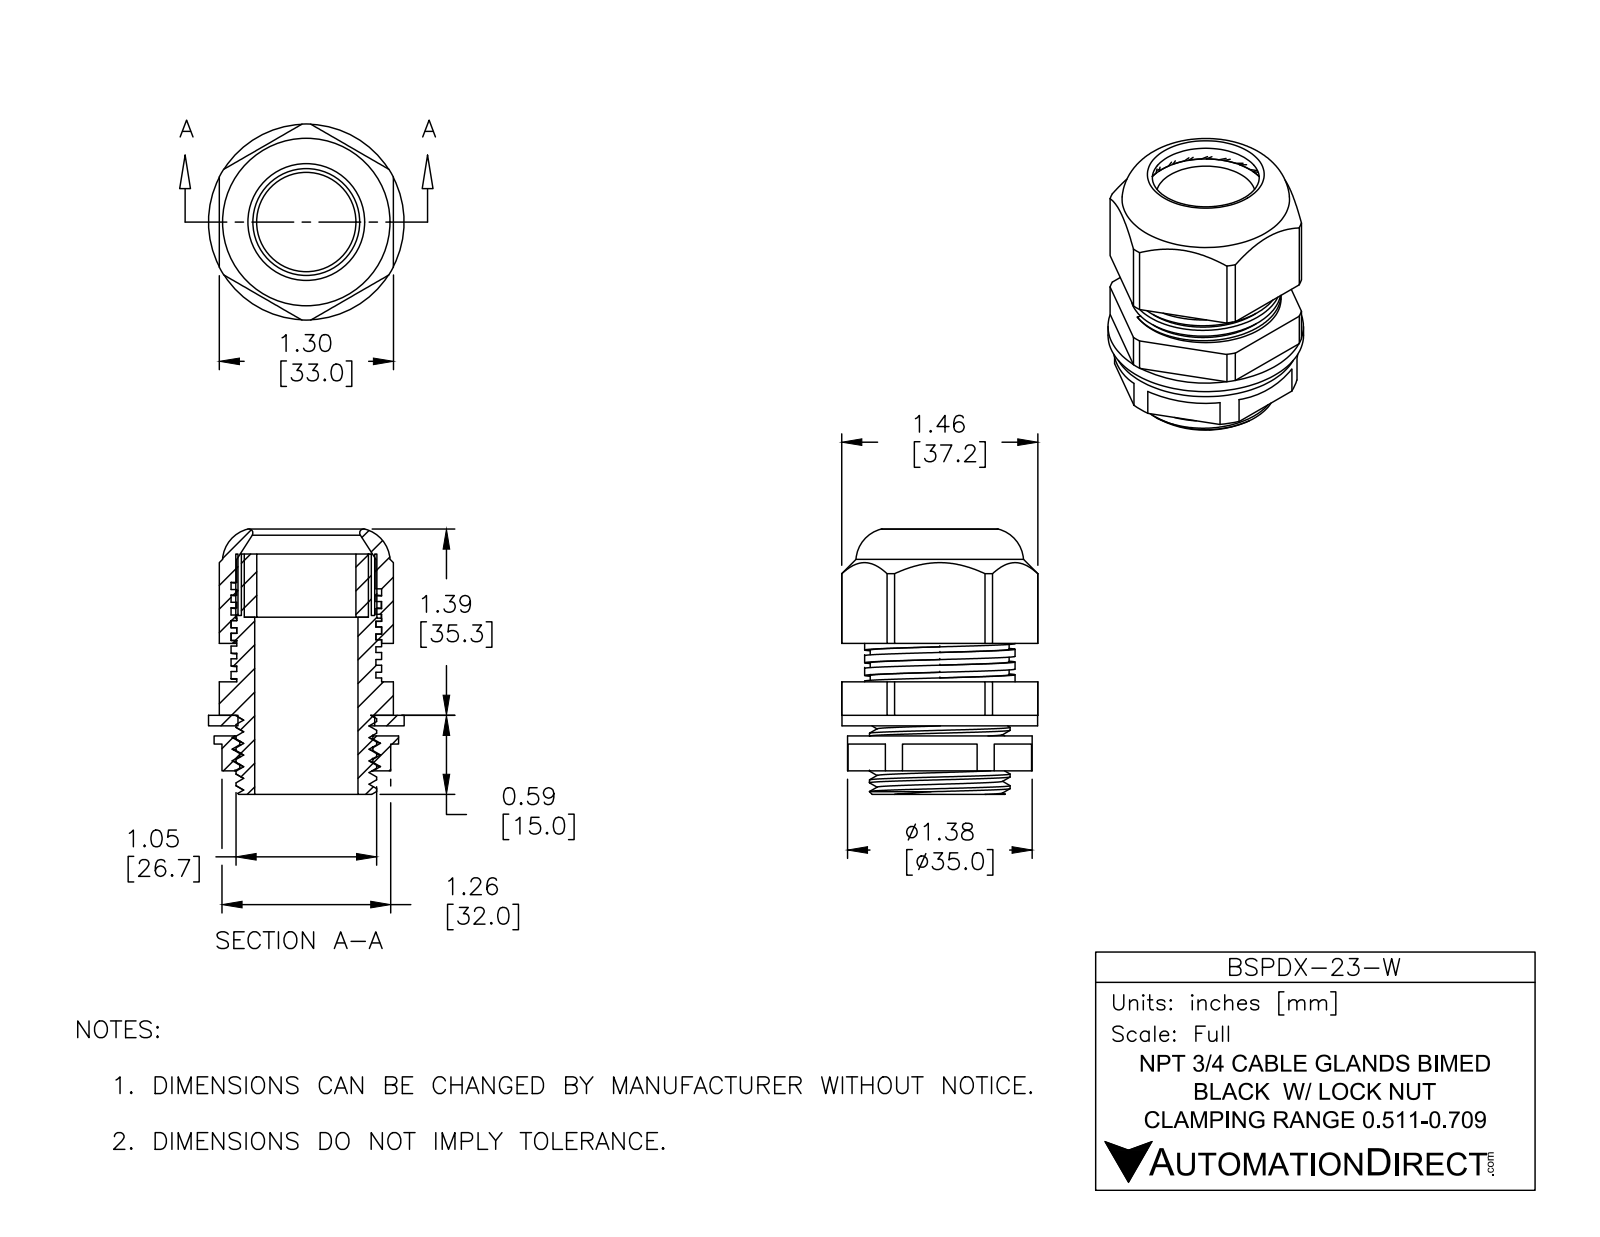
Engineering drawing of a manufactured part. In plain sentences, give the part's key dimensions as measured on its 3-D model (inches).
The part is named "BSPDX-23-W". Its 3-D file was written by "SolidWorks 2015 (CONFIG_CONTROL_DESIGN)". It is 5 solids with 224 faces: 126 planar, 74 cylindrical and 24 other. Overall it measures 1.981 by 1.464 by 1.46 inches. Its volume is 1.484 cubic inches and its surface area 35.03 square inches. Round holes: 1 of diameter 0.741, 1 of diameter 0.771, 1 of diameter 0.927, 1 of diameter 0.993, 1 of diameter 1.02, 1 of diameter 1.039. Round bosses or shafts: 1 of diameter 1.46, 1 of diameter 1.378, 1 of diameter 1.123, 1 of diameter 1.053, 1 of diameter 1.05. Partial cylindrical surfaces (rounded edges, fillets, slot ends): 1 of radius 0.732. The main face-to-face distances are 1.299, 0.02, 0.079, 0.02, 1.28, 0.125, 0.204, 0.783, 0.454, 0.329.
